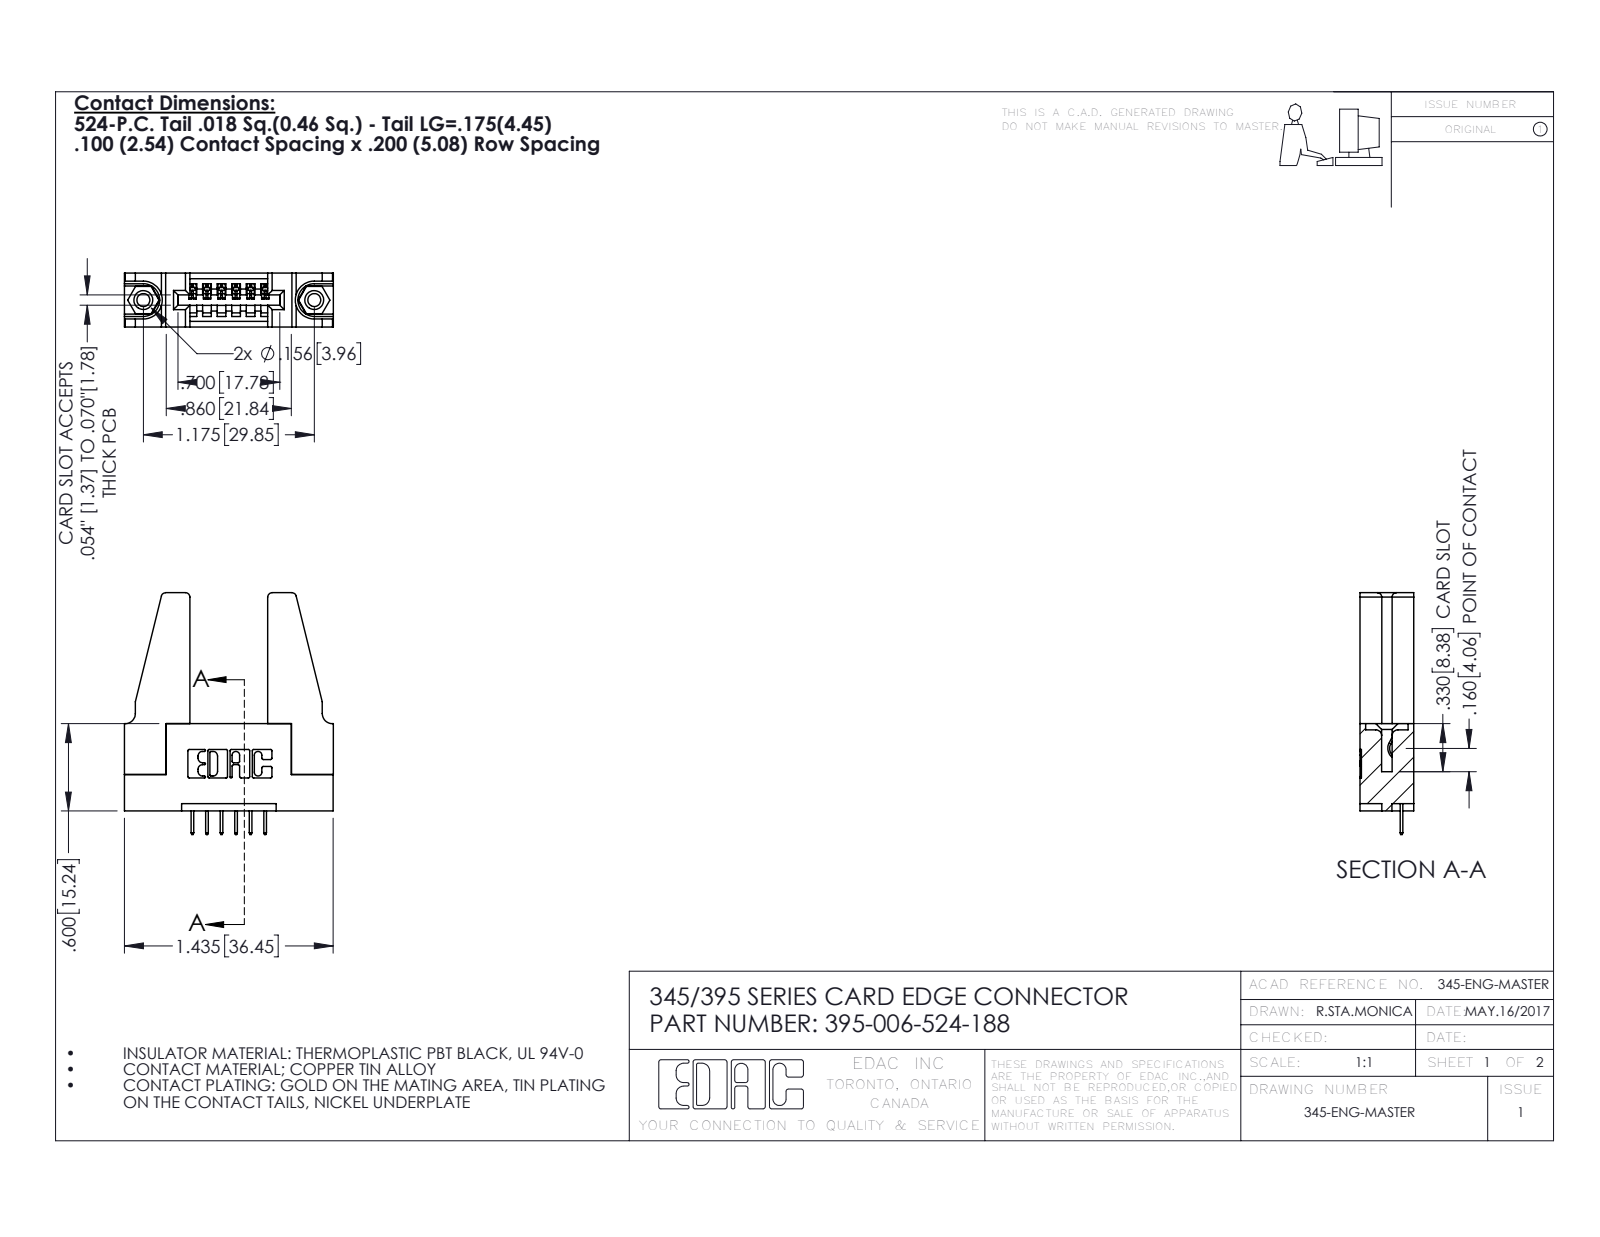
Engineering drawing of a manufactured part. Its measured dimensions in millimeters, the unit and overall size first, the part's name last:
Units: millimetres
Overall size (bounding box): 42.2 × 36.5 × 9.4
Round holes (diameter × count): ⌀2.3 ×2, ⌀3.2 ×2, ⌀4 ×2, ⌀1.6 ×1
Round bosses / shafts (diameter × count): ⌀3.9 ×2
Partial cylindrical surfaces — rounded edges, fillets, slot ends (radius × count): R0.3 ×22, R0.2 ×12, R0.8 ×8, R0.2 ×6, R0.8 ×6, R0.7 ×3, R0.8 ×2, R1 ×2
Main face-to-face distances: 9.4, 5.1, 1.8, 7.6, 17.7, 3.8, 3.8, 8.9, 6.4, 2
Hole centre spacings: 6.9, 24, 29.8
Volume: 6 390 mm³ · Surface area: 6 742 mm²
Bodies: 11 solids, 622 faces (428 planar, 178 cylindrical, 16 other)
Part name (STEP PRODUCT): 345-250-001_345-250-001-102; 345-292-001_345-293-124; 345-220-078_345-220-088; 395-006-524-188 (+1 more)
STEP written by: SolidWorks 2016 (CONFIG_CONTROL_DESIGN)
